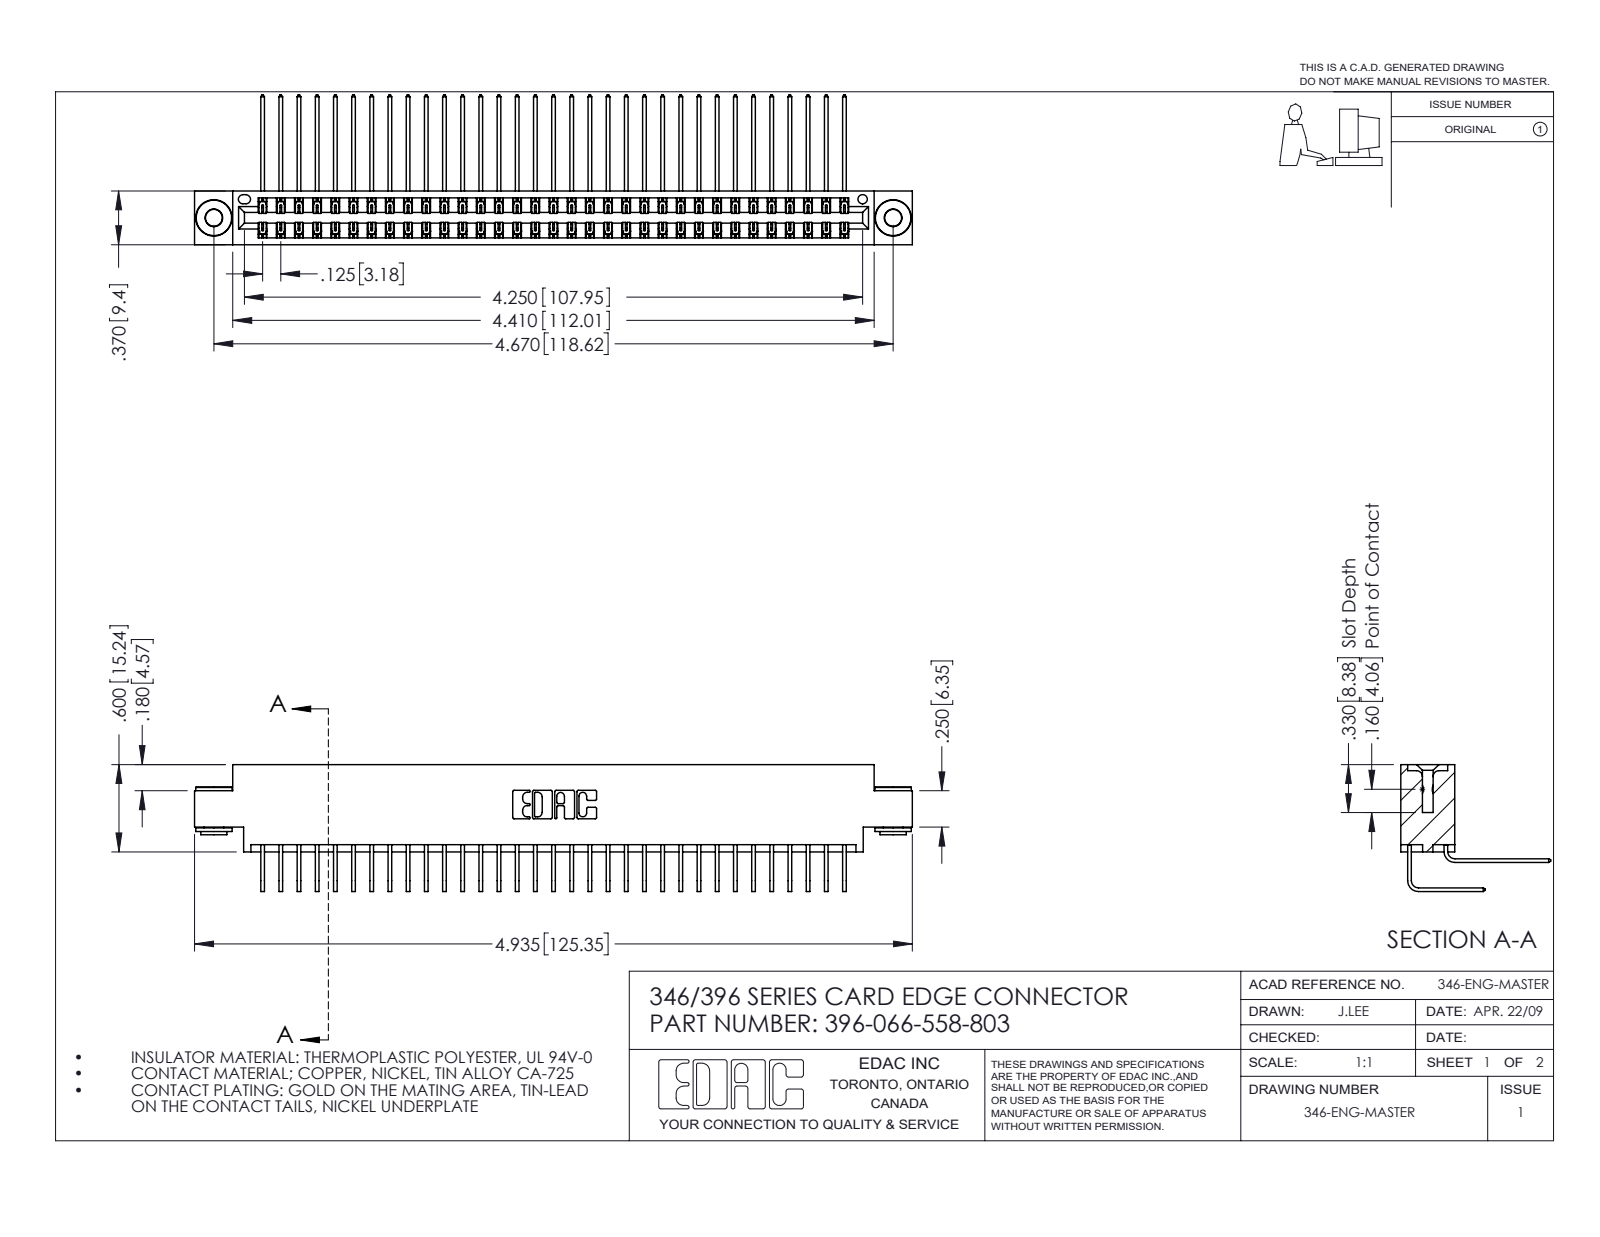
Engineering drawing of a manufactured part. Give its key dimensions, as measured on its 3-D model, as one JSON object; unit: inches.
{"part_name": "396-066-558-803; 345-292-001_558 Tail - 2; 345-250-002_345-250-002-102; 345-292-001_558 559 Tail - 1 (+1 more)", "step_written_by": "SolidWorks 2016 (CONFIG_CONTROL_DESIGN)", "units": "inches", "bodies": {"solids": 69, "faces": 3728, "planar": 2532, "cylindrical": 1188, "other": 8}, "overall_size": [4.935, 1.03, 0.873], "volume_in3": 0.757, "surface_area_in2": 29.64, "round_holes": [[0.116, 2], [0.156, 2], [0.064, 1]], "round_bosses_or_shafts": [[0.25, 2], [0.18, 2], [0.136, 2]], "partial_cylinders_radius": [[0.006, 99], [0.01, 22], [0.007, 6], [0.031, 6], [0.026, 3], [0.014, 2], [0.022, 2], [0.024, 2]], "face_to_face_distances": [0.322, 0.048, 0.025, 0.37, 0.25, 0.298, 0.072, 0.275, 0.148, 0.222], "hole_center_spacings": [0.246, 4.462, 4.67]}
